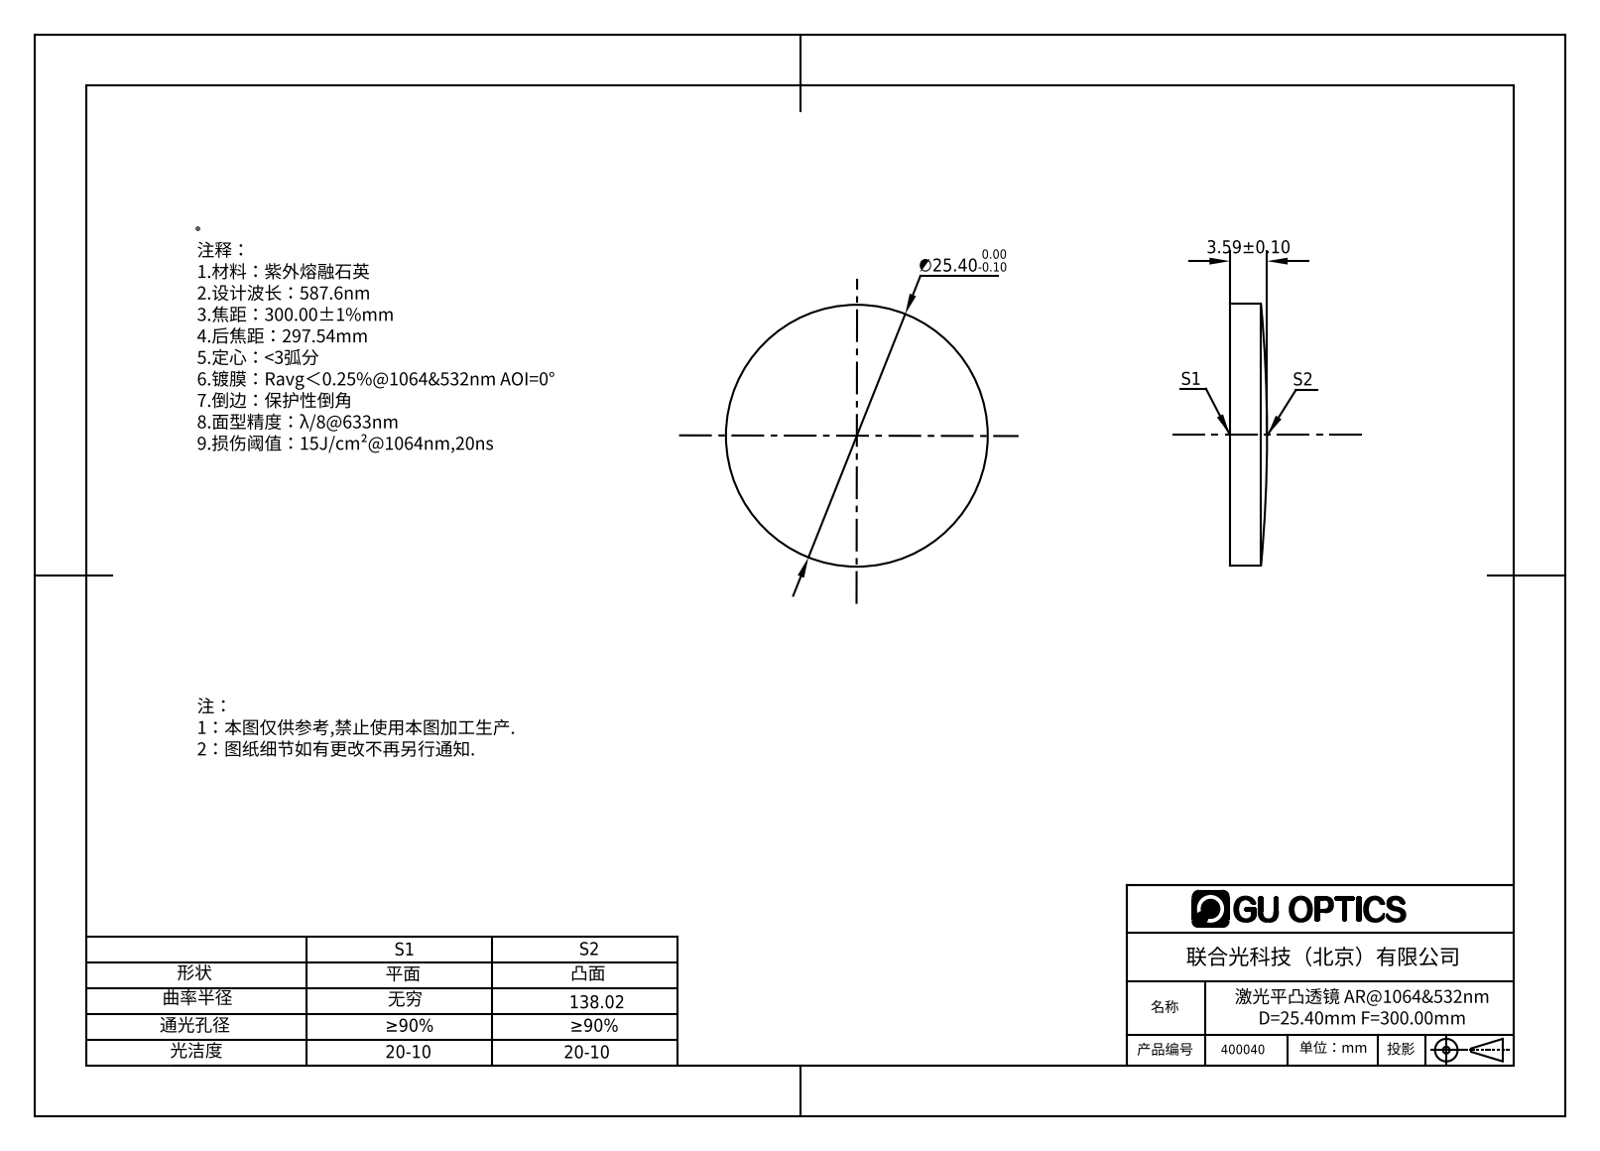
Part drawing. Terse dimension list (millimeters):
name: 400023
written by: SolidWorks 2016 (AUTOMOTIVE_DESIGN)
unit: mm
bodies: 1 solid, 5 faces (1 planar, 2 cylindrical, 2 other)
size: 25.4 × 25.4 × 3.59
volume: 1 669 mm³; area: 1 254 mm²
bosses: 1× ⌀25.4
